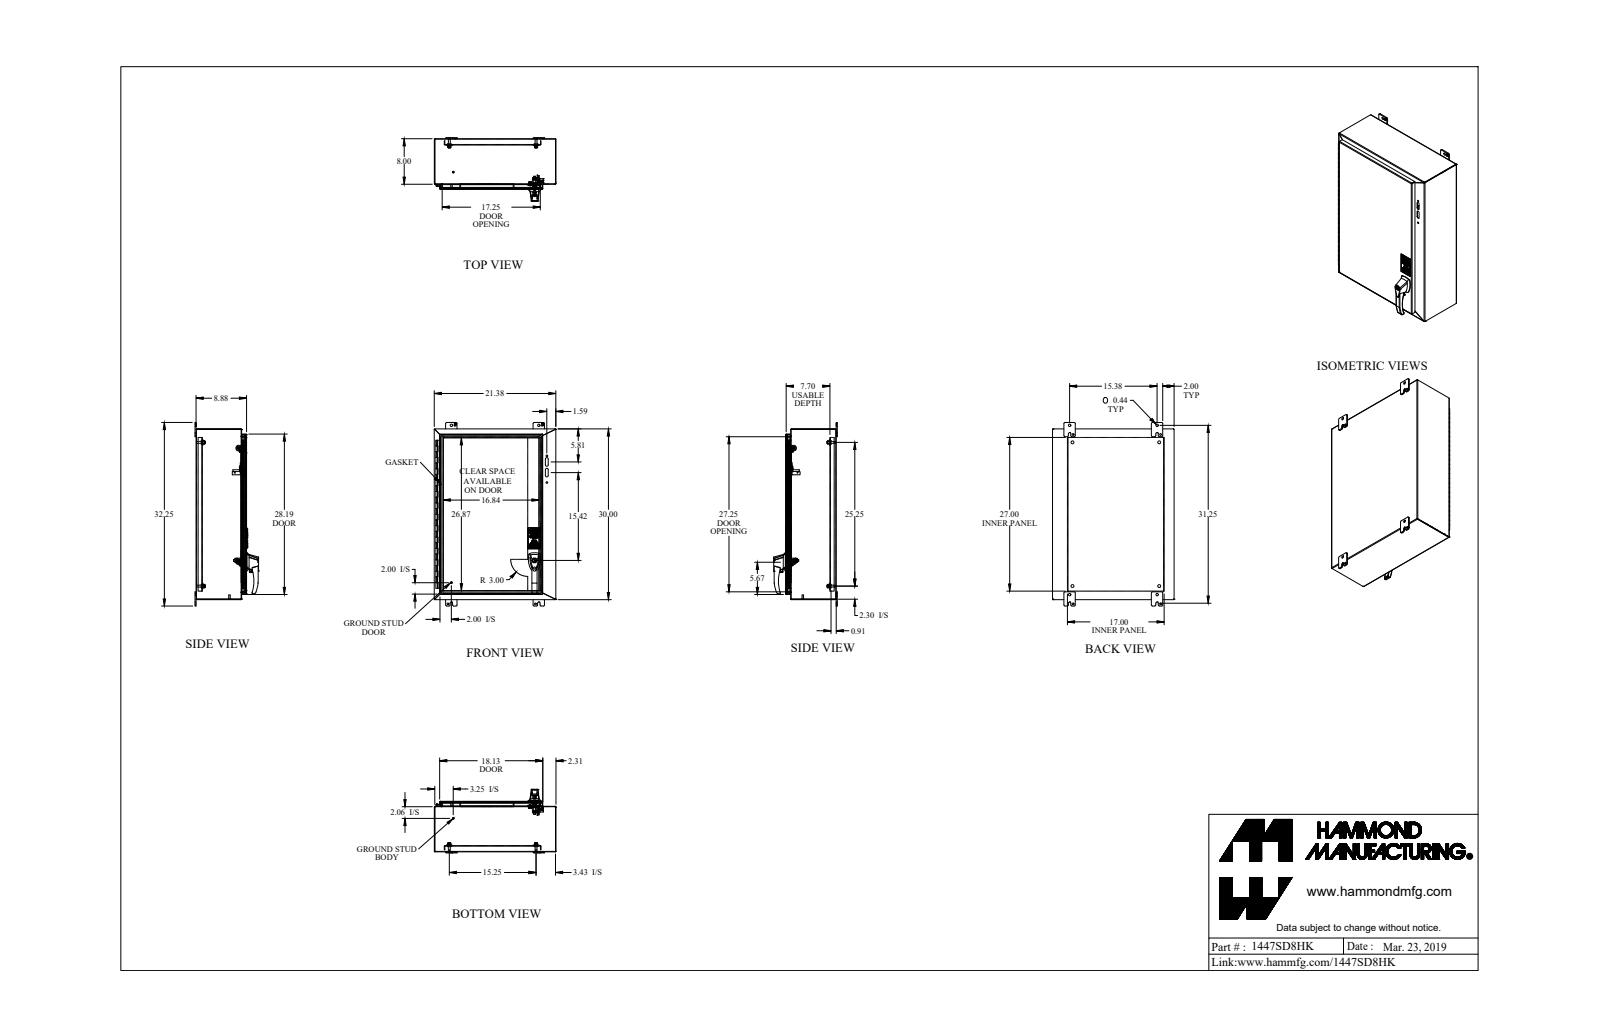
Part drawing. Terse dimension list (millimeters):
name: 1447SD8HK
written by: SolidWorks 2019 (AUTOMOTIVE_DESIGN)
unit: mm
bodies: 49 solids, 1193 faces (735 planar, 343 cylindrical, 115 other)
size: 819.14 × 542.93 × 283.9
volume: 3 969 000 mm³; area: 3 907 000 mm²
holes: 5× ⌀7.94, 4× ⌀4.47, 4× ⌀11.11, 4× ⌀12.7, 2× ⌀3.97, 2× ⌀4.39, 2× ⌀5.46, 2× ⌀6.35, 2× ⌀6.73, 2× ⌀7.14, 2× ⌀7.81, 2× ⌀10.49
bosses: 8× ⌀9.53, 7× ⌀6.35, 4× ⌀25.4, 4× ⌀16.51, 4× ⌀8.38, 4× ⌀3.97, 2× ⌀12.7, 2× ⌀10.21
rounds: 28× R2, 24× R4.76, 16× R0.17, 12× R6.35, 11× R3.17, 8× R0.76, 8× R3.83, 8× R5.54
face distances: 1.83, 223.6, 221.77, 225.43, 2.41, 541.1, 197.39, 195.56, 26.21, 28.04
hole spacings: 390.53, 28.21, 44.08, 44.09, 315.79, 372.73, 377.31, 387.35
